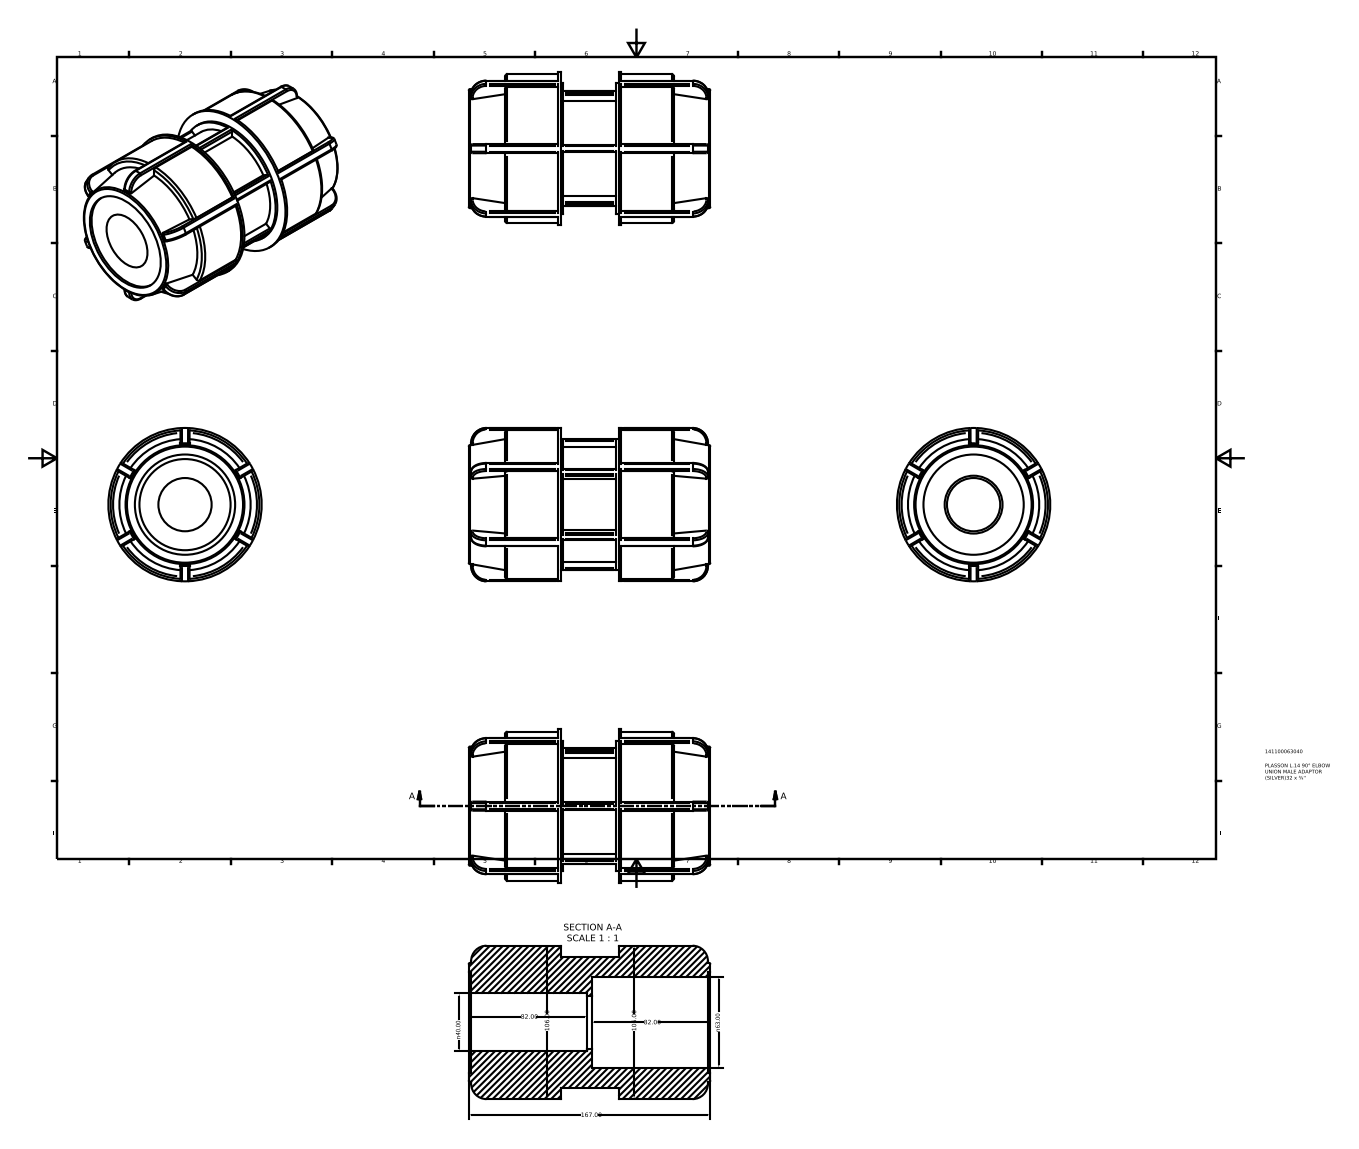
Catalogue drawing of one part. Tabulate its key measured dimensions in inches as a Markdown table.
| quantity | value |
| --- | --- |
| part name | 141100063040 |
| STEP written by | Autodesk Inventor 2015 (AUTOMOTIVE_DESIGN) |
| units | inches |
| bodies | 1 solid, 230 faces (92 planar, 86 cylindrical, 52 other) |
| overall size | 6.575 × 4.173 × 4.173 |
| volume | 48.49 in³ |
| surface area | 160.5 in² |
| round holes (diameter × count) | 1.449 × 1, 1.575 × 1, 2.48 × 1, 2.728 × 1 |
| round bosses / shafts (diameter × count) | 4.173 × 1, 4.048 × 1, 3.547 × 1, 3.13 × 1 |
| partial cylindrical surfaces (radius × count) | 0.042 × 44 |
| main face-to-face distances | 1.578, 4.011, 0.066, 1.512, 2.498, 2.433, 4.076, 2.564, 0.248, 0.986 |
